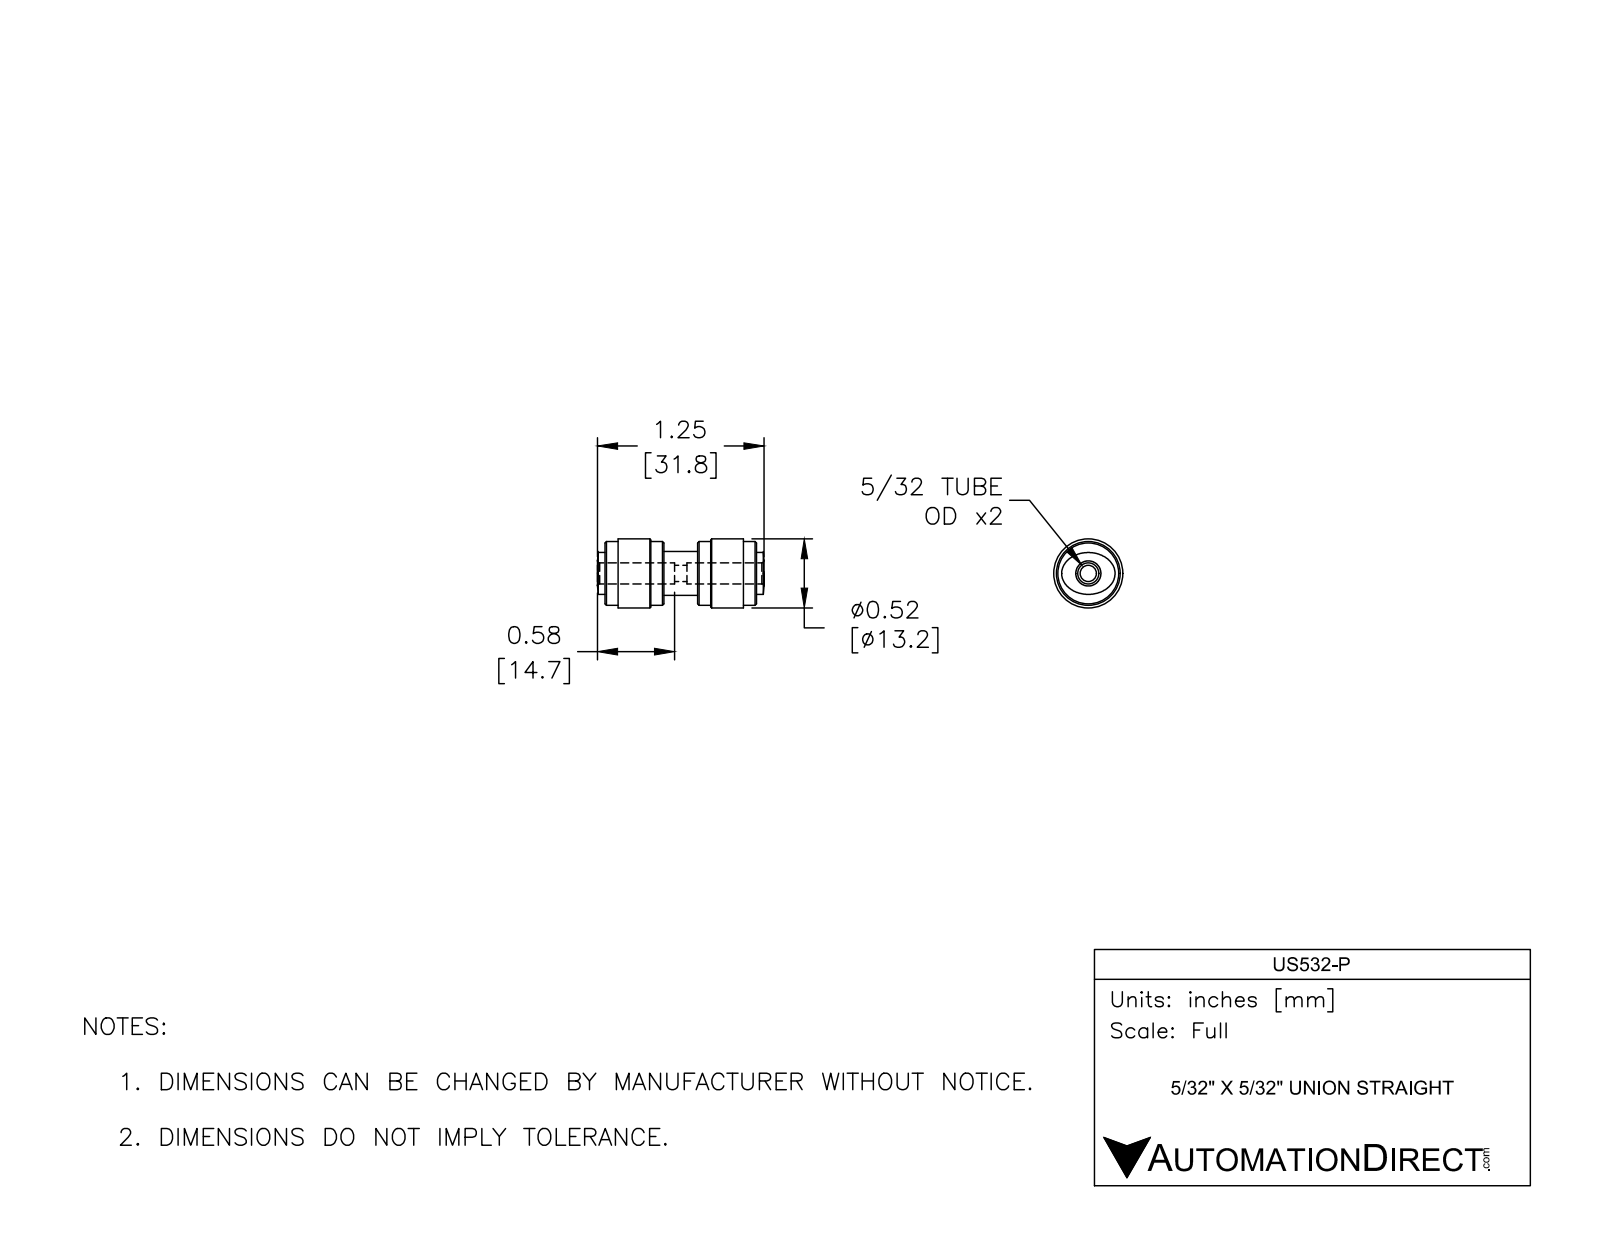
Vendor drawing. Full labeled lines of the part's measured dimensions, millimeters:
Part name (STEP PRODUCT): US532-P
STEP written by: SolidWorks 2017 (AUTOMOTIVE_DESIGN)
Units: millimetres
Bodies: 1 solid, 54 faces (10 planar, 20 cylindrical, 24 other)
Overall size (bounding box): 31.8 × 13.2 × 13.2
Volume: 3 020 mm³ · Surface area: 1 919 mm²
Round holes (diameter × count): ⌀3.1 ×1, ⌀4 ×1
Round bosses / shafts (diameter × count): ⌀13.2 ×1, ⌀12.2 ×1, ⌀8.4 ×1
Main face-to-face distances: 17.7, 11.3, 2.5, 8.8, 6.4, 29, 26.5, 15.2, 20.2, 6.3
